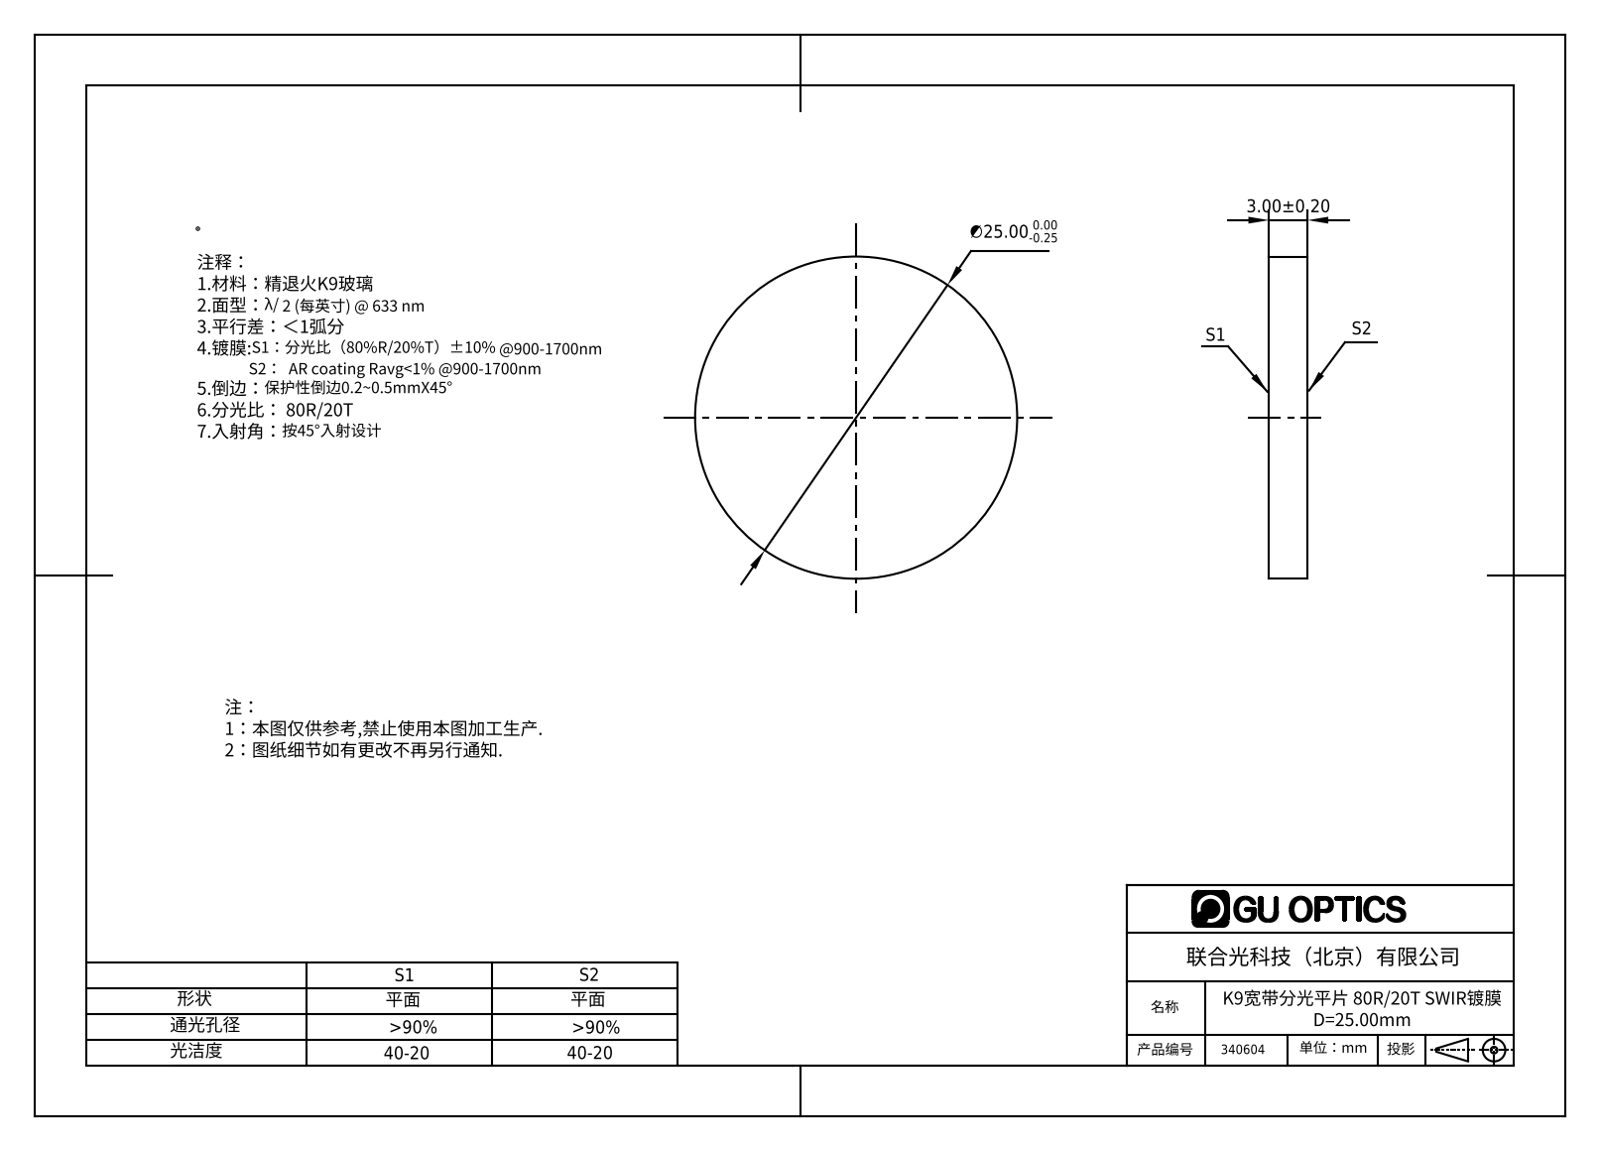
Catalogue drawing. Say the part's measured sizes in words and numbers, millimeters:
The part is named "340514". Its 3-D file was written by "SolidWorks 2016 (CONFIG_CONTROL_DESIGN)". It is 1 solid with 4 faces: 2 planar, 2 cylindrical and 0 other. Overall it measures 25 by 25 by 3 millimeters. Its volume is 1 473 cubic millimeters and its surface area 1 217 square millimeters. Round bosses or shafts: 1 of diameter 25. The main face-to-face distances are 3.
